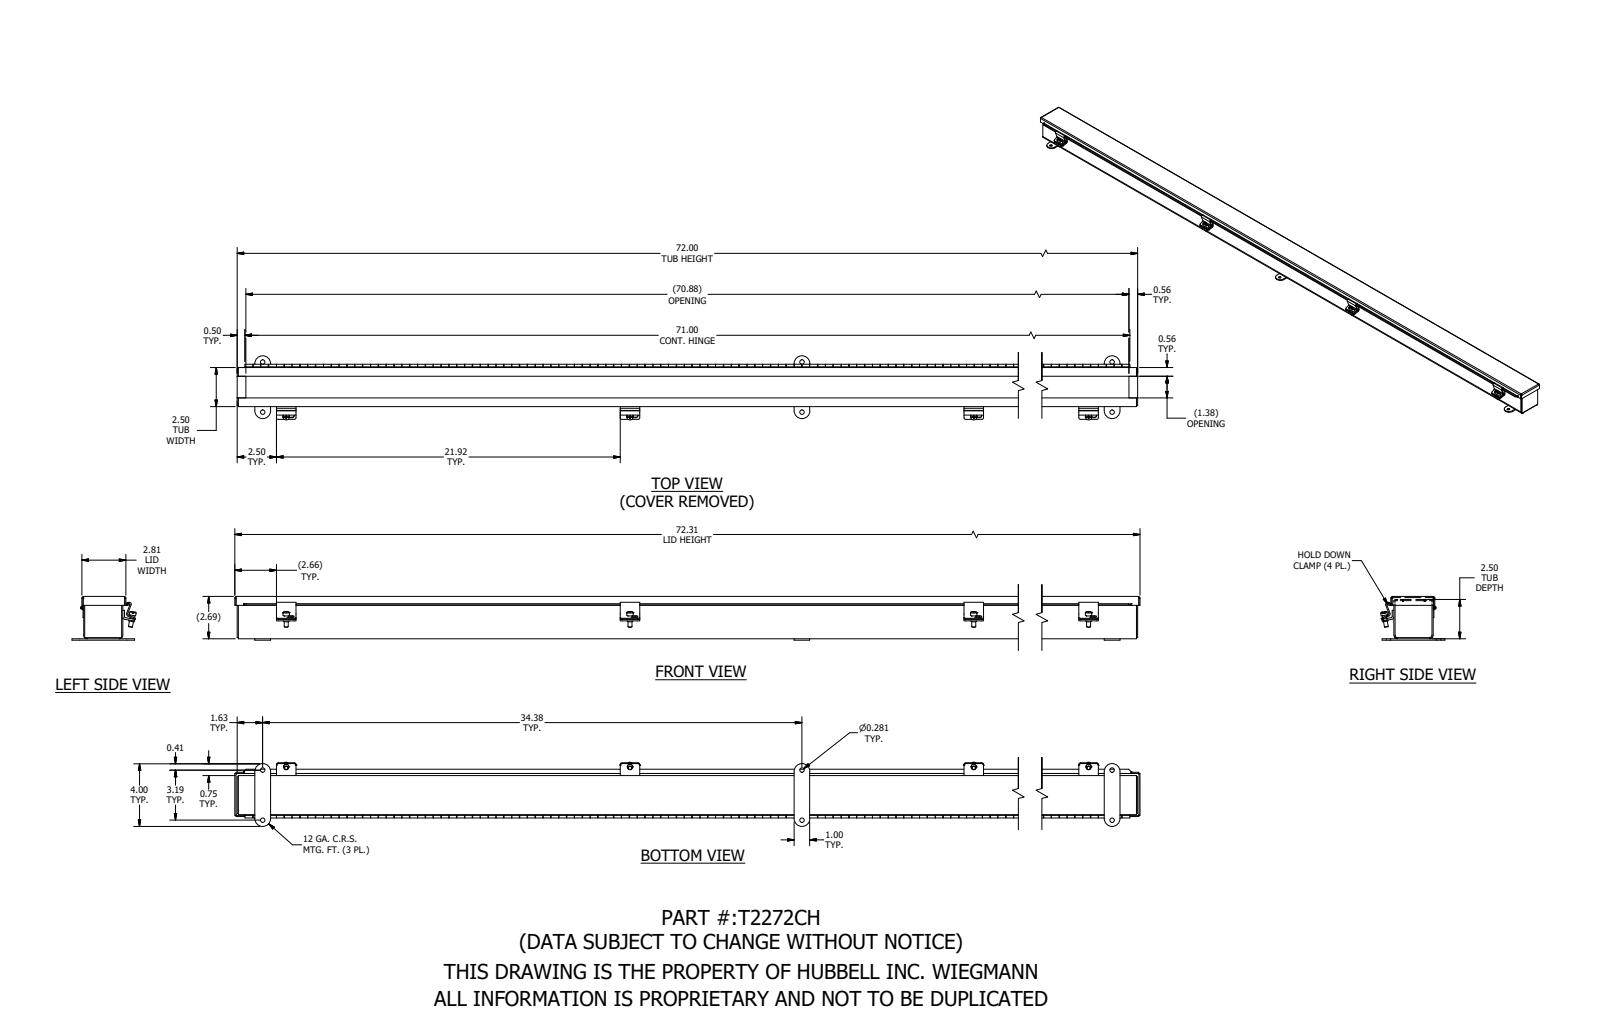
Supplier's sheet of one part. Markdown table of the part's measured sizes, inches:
| quantity | value |
| --- | --- |
| part name | T2272CH |
| STEP written by | SolidWorks 2021 (AUTOMOTIVE_DESIGN) |
| units | inches |
| bodies | 22 solids, 1389 faces (664 planar, 697 cylindrical, 28 other) |
| overall size | 72.313 × 4.095 × 2.783 |
| volume | 72.52 in³ |
| surface area | 2 092 in² |
| round holes (diameter × count) | 0.281 × 6, 0.196 × 4, 0.116 × 1 |
| round bosses / shafts (diameter × count) | 0.41 × 4, 0.344 × 4, 0.25 × 4, 0.2 × 1, 0.1 × 1 |
| partial cylindrical surfaces (radius × count) | 0.125 × 16, 0.031 × 9, 0.105 × 9, 0.133 × 8, 0.5 × 6, 0.063 × 3, 0.126 × 3, 0.156 × 2 |
| main face-to-face distances | 0.074, 2.426, 2.615, 2.5, 2.352, 2.689, 2.541, 2.542, 0.116, 0.189 |
| hole center spacings | 3.187, 21.917, 34.375, 34.375, 34.522, 34.523, 68.75, 68.824 |
